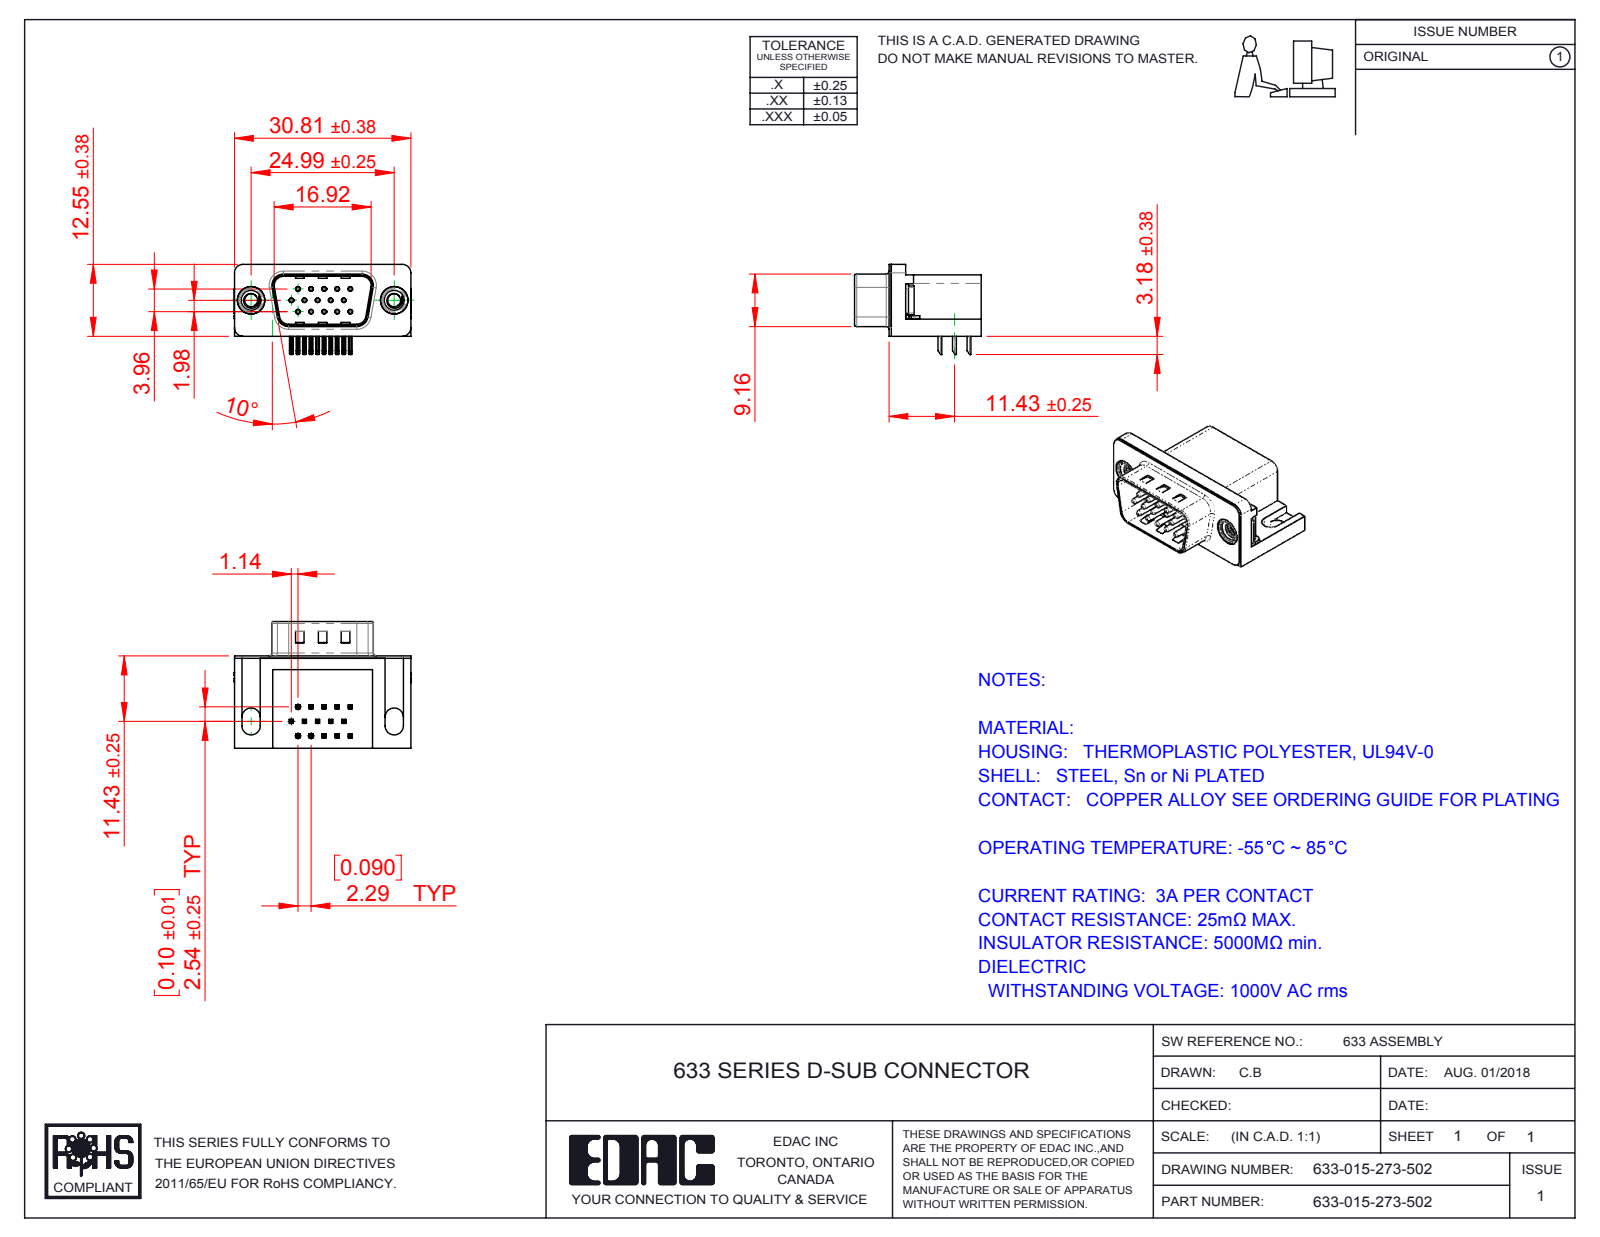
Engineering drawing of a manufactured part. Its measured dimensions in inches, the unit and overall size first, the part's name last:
Units: inches
Overall size (bounding box): 1.216 × 0.87 × 0.619
Round holes (diameter × count): ⌀0.014 ×15, ⌀0.031 ×15, ⌀0.089 ×2, ⌀0.157 ×2, ⌀0.189 ×2, ⌀0.197 ×2
Round bosses / shafts (diameter × count): ⌀0.03 ×15, ⌀0.193 ×2, ⌀0.187 ×2, ⌀0.154 ×2
Partial cylindrical surfaces — rounded edges, fillets, slot ends (radius × count): R0.01 ×68, R0.005 ×30, R0.039 ×16, R0.02 ×9, R0.063 ×8, R0.059 ×7, R0.035 ×4, R0.079 ×4
Main face-to-face distances: 0.016, 0.407, 0.618, 0.114, 0.264, 0.634, 0.098, 0.014, 0.421, 0.52
Hole centre spacings: 0.156, 0.09, 0.18, 0.09, 0.238, 0.27, 0.312, 0.238
Volume: 0.246 in³ · Surface area: 8.057 in²
Bodies: 21 solids, 1439 faces (861 planar, 439 cylindrical, 139 other)
Part name (STEP PRODUCT): 633 Contact Middle_Recessed; 633 Contact Top; 633 Contact Bottom; 633-015-273-502 (+5 more)
STEP written by: SolidWorks 2016 (CONFIG_CONTROL_DESIGN)
